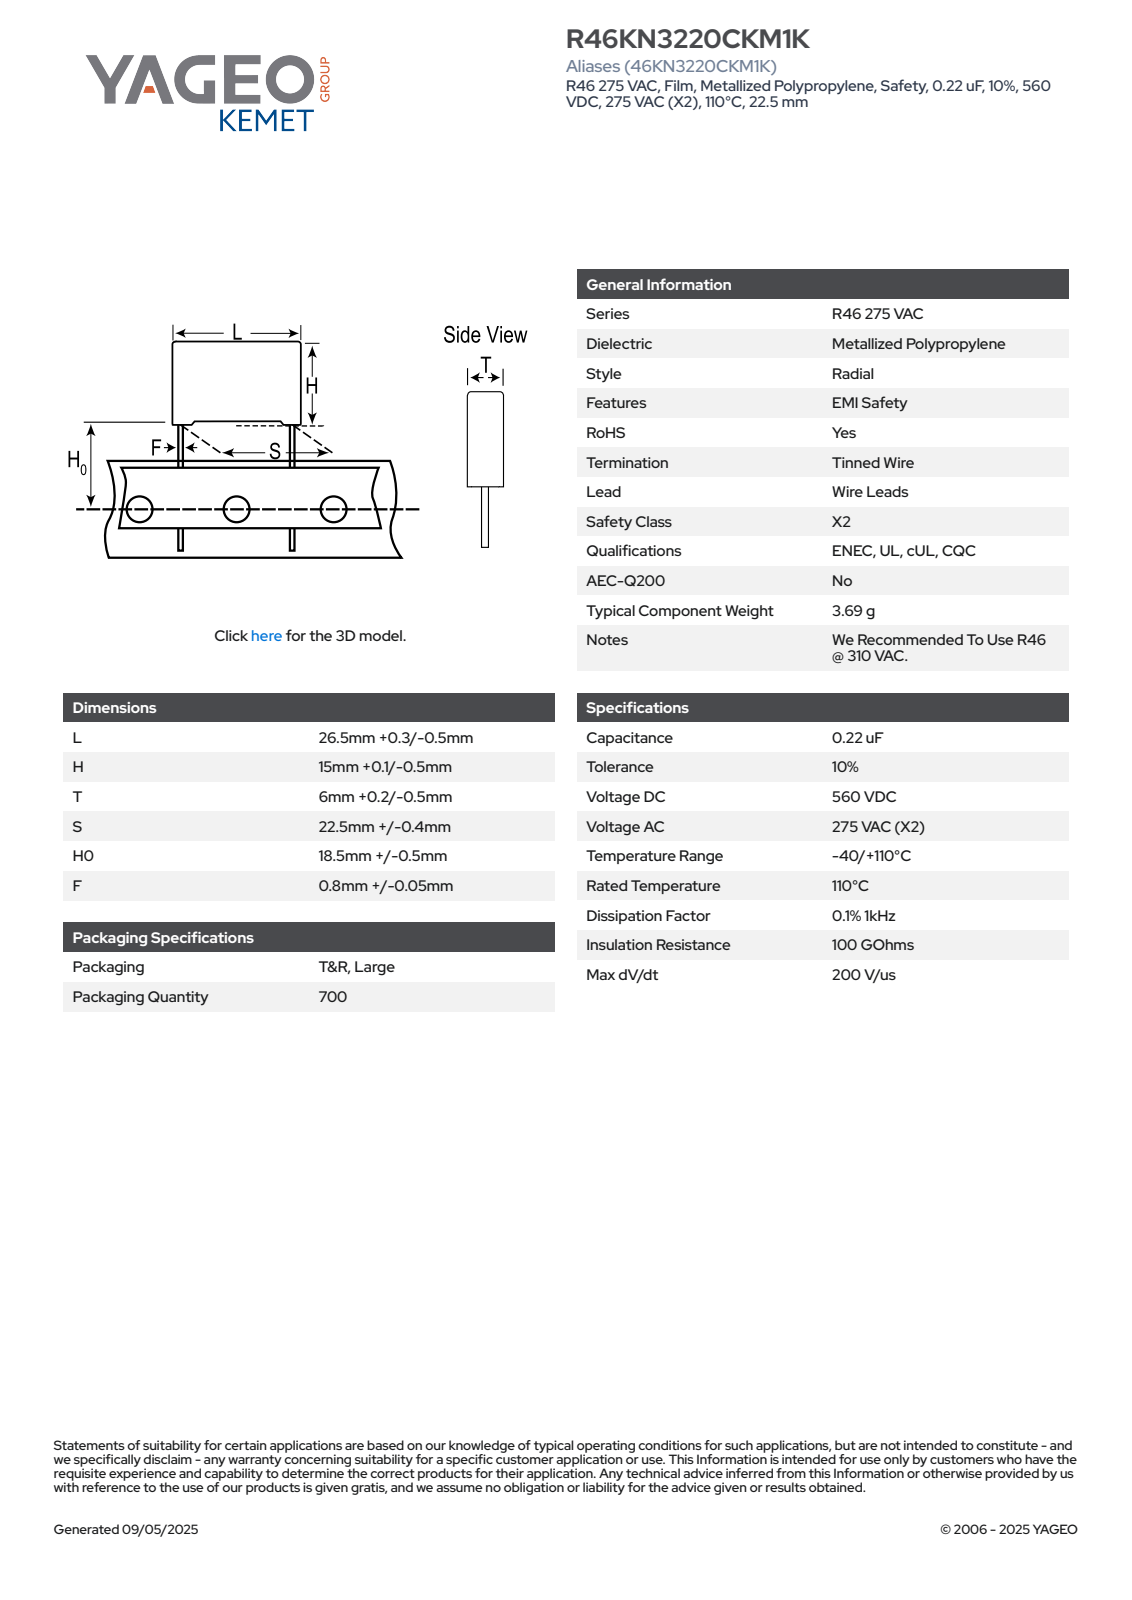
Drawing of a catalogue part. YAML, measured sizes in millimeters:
part_name: "CFR_RB2_26.5X15X6_L26.8H15.1T6.2S22.5H019F0.85"
step_written_by: "SolidWorks 2020 (AUTOMOTIVE_DESIGN)"
units: millimeters
bodies: {solids: 4, faces: 85, planar: 77, cylindrical: 8, other: 0}
overall_size: [34.1, 26.8, 6.21]
volume: 2428
surface_area: 1480
round_bosses_or_shafts:
  - {diameter: 0.85, count: 2}
partial_cylinders:
  - {radius: 0.5, count: 4}
face_to_face_distances: [6.2, 14.35, 26.8, 14.58, 0.89, 0.52, 0.75, 15.1, 5.31, 4.42]
